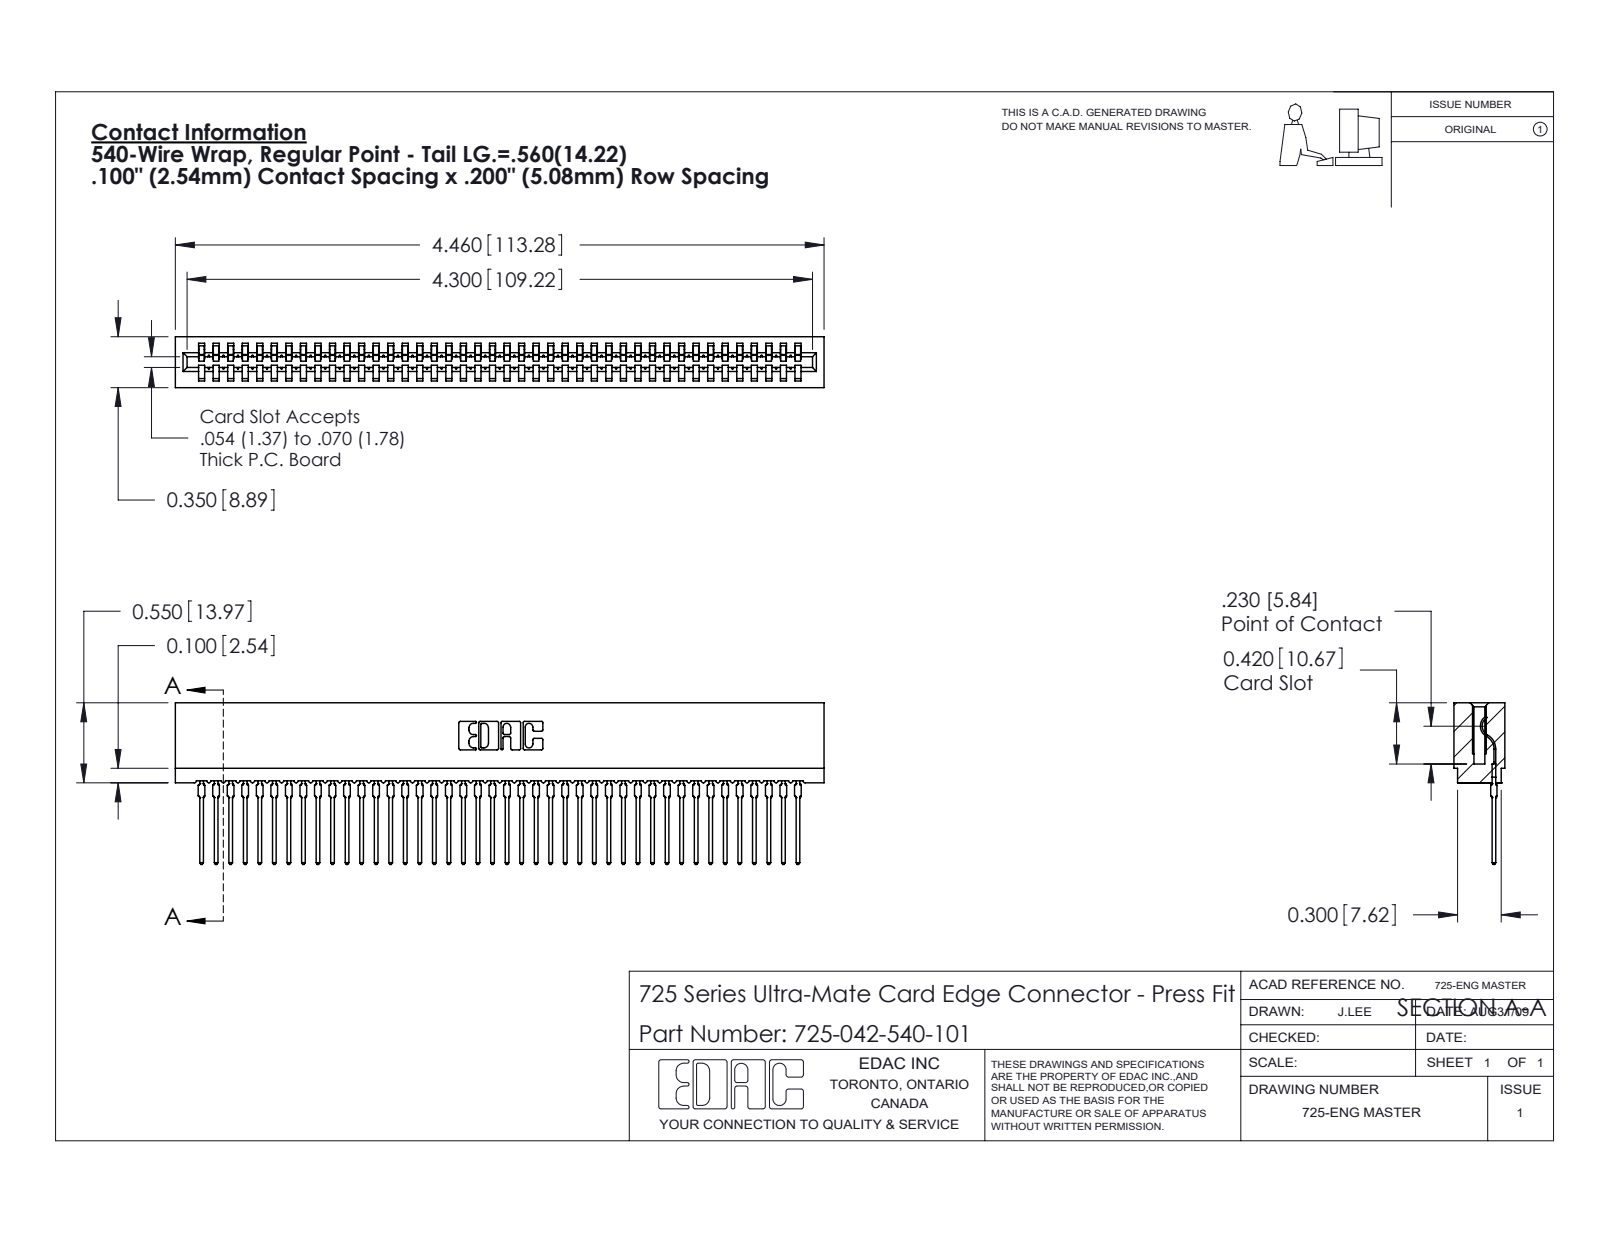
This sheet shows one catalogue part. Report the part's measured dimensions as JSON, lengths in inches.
{"part_name": "725-042-540-101; 725 Part_Insulator Option - 01; 745-292-001_540", "step_written_by": "SolidWorks 2020 (CONFIG_CONTROL_DESIGN)", "units": "inches", "bodies": {"solids": 43, "faces": 4799, "planar": 2869, "cylindrical": 838, "other": 1092}, "overall_size": [4.46, 1.111, 0.35], "volume_in3": 0.531, "surface_area_in2": 26.65, "partial_cylinders_radius": [[0.015, 84], [0.021, 84], [0.01, 22], [0.007, 6], [0.031, 6], [0.005, 4], [0.011, 4], [0.026, 3]], "face_to_face_distances": [0.35, 0.212, 0.138, 0.063, 0.287, 0.2, 0.045, 0.305, 0.093, 0.167]}
